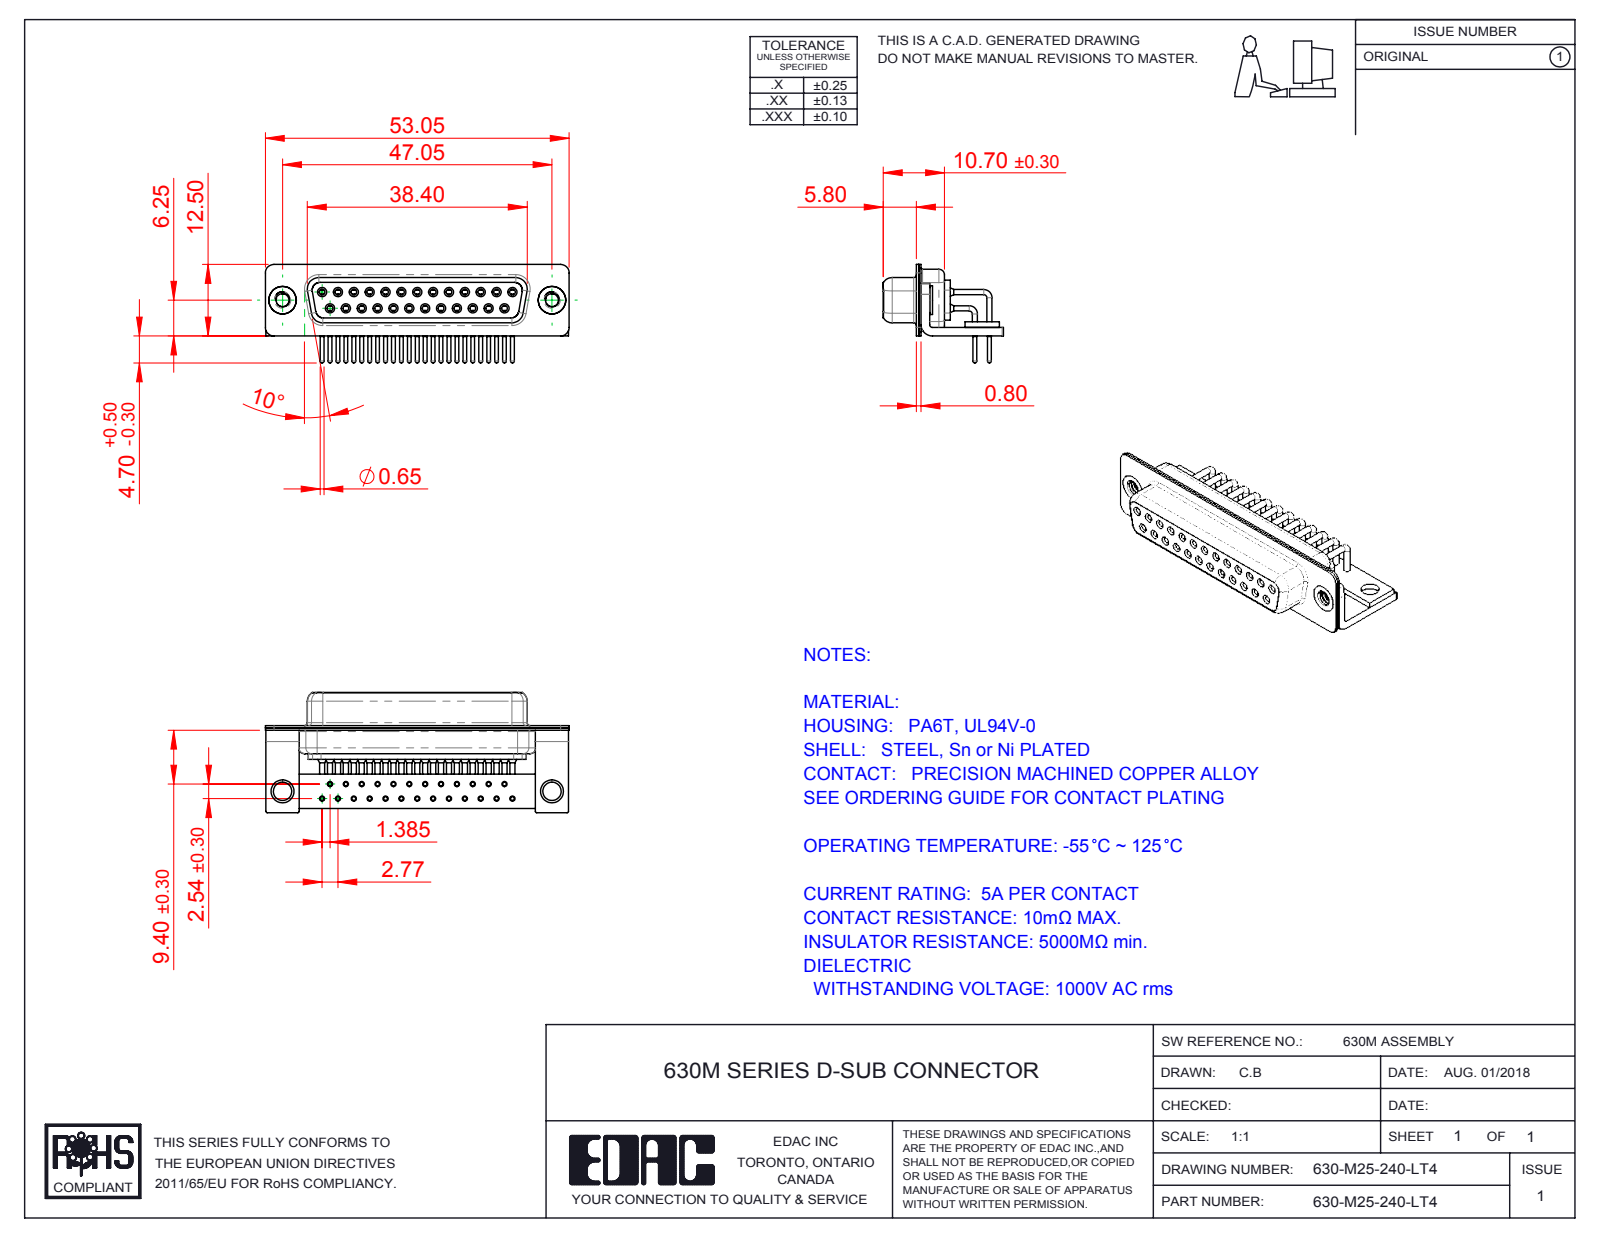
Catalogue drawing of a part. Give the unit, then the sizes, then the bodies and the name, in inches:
Units: inches
Overall size (bounding box): 2.089 × 0.827 × 0.677
Round holes (diameter × count): ⌀0.035 ×25, ⌀0.039 ×25, ⌀0.043 ×25, ⌀0.067 ×25, ⌀0.071 ×25, ⌀0.079 ×25, ⌀0.089 ×2, ⌀0.126 ×2, ⌀0.157 ×2, ⌀0.189 ×2
Round bosses / shafts (diameter × count): ⌀0.063 ×25, ⌀0.059 ×25, ⌀0.035 ×25, ⌀0.026 ×25, ⌀0.197 ×2, ⌀0.193 ×2
Partial cylindrical surfaces — rounded edges, fillets, slot ends (radius × count): R0.01 ×16, R0.059 ×16, R0.079 ×13, R0.053 ×10, R0.063 ×8, R0.02 ×5, R0.024 ×4, R0.026 ×4
Main face-to-face distances: 0.016, 0.091, 0.075, 0.057, 0.352, 0.033, 0.368, 0.031, 0.244, 0.039
Hole centre spacings: 0.109, 0.218, 0.327, 0.436, 0.545, 0.124, 0.192, 0.654
Volume: 0.272 in³ · Surface area: 17.2 in²
Bodies: 33 solids, 1704 faces (468 planar, 784 cylindrical, 452 other)
Part name (STEP PRODUCT): 630M 4-40 Threaded Rivet_Stabilizer; 630M Contact Row 1; 630-M25-240-LT4; 630M Housing_25 Contacts (+5 more)
STEP written by: SolidWorks 2016 (CONFIG_CONTROL_DESIGN)
